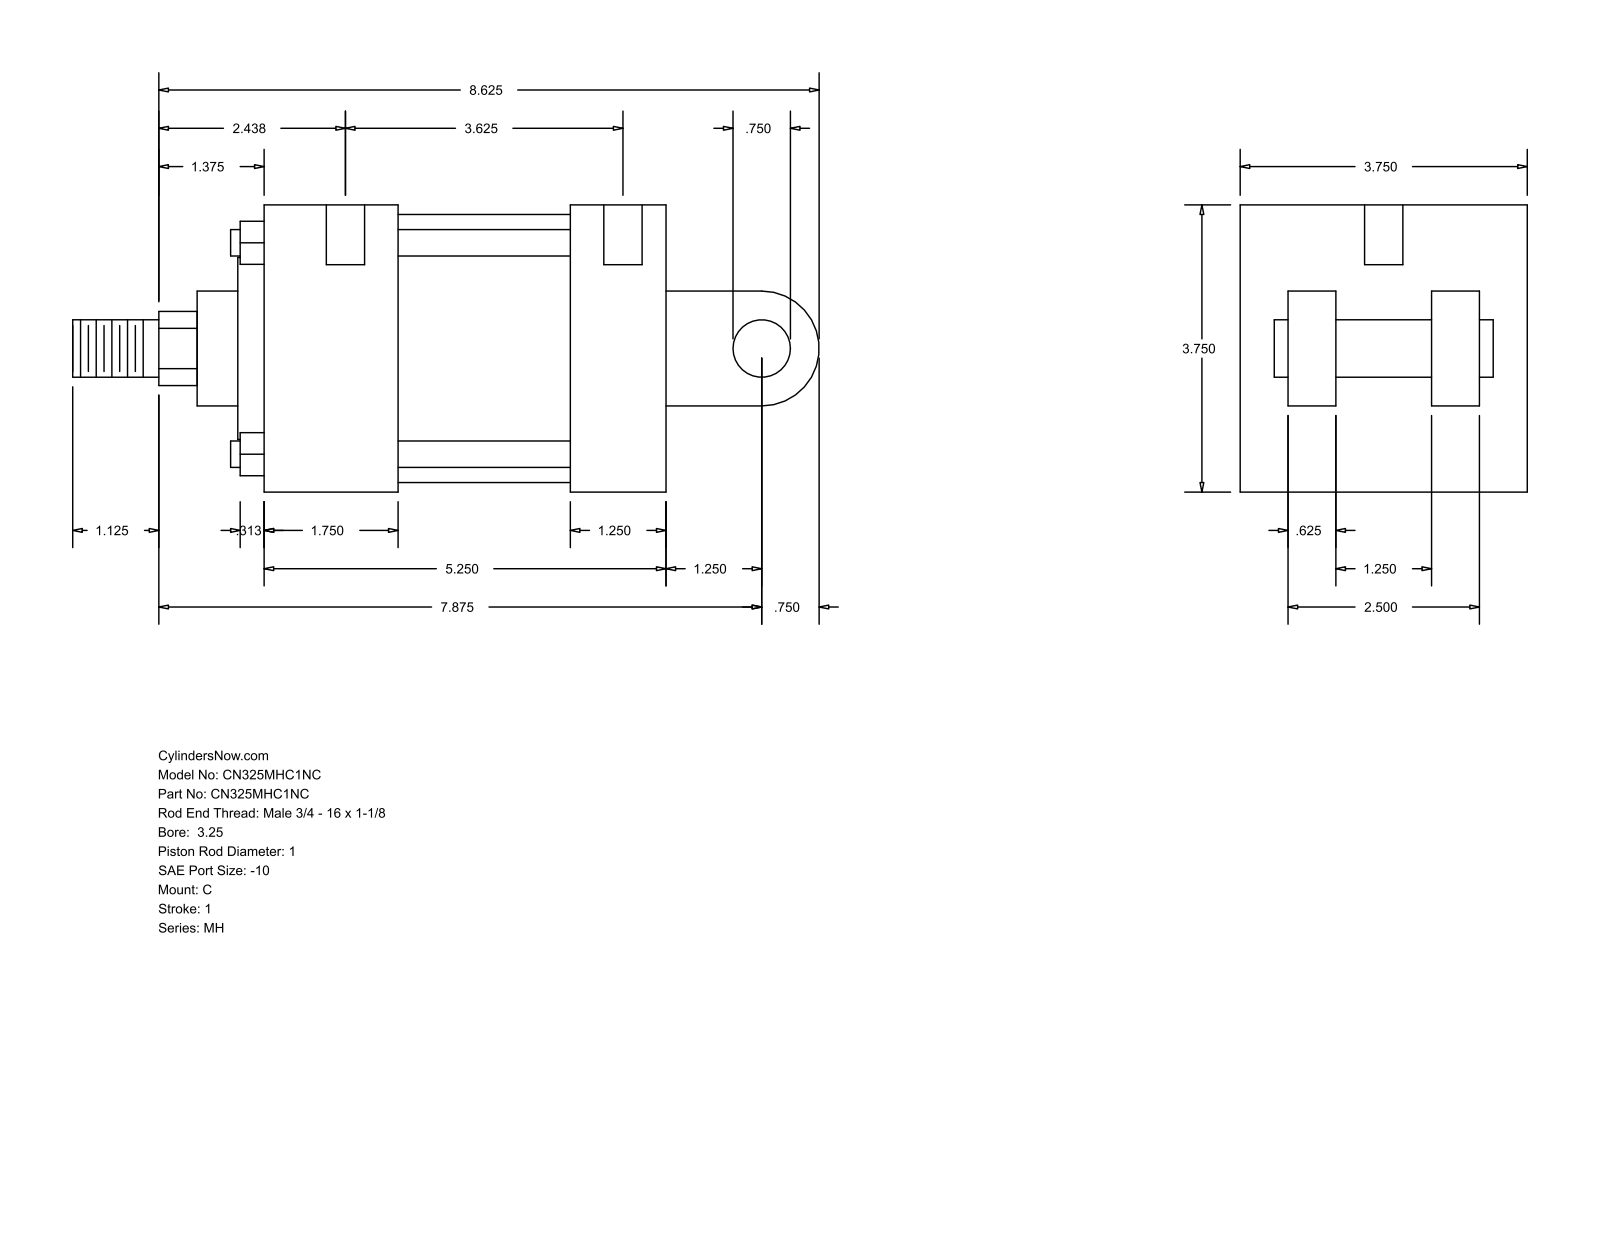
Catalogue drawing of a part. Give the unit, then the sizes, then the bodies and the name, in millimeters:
Units: millimetres
Overall size (bounding box): 247.65 × 95.25 × 95.25
Round holes (diameter × count): ⌀5.56 ×4, ⌀12.7 ×2
Round bosses / shafts (diameter × count): ⌀8.76 ×4, ⌀19.05 ×2, ⌀88.9 ×1, ⌀60.33 ×1, ⌀38.1 ×1, ⌀25.4 ×1
Partial cylindrical surfaces — rounded edges, fillets, slot ends (radius × count): R12.29 ×1, R19.05 ×1
Main face-to-face distances: 95.24, 15.87, 133.36, 63.5, 79.37, 31.74, 47.63, 44.46, 101.61, 57.15
Hole centre spacings: 98.42, 1.58, 4.76, 92.08, 93.66, 96.84
Bodies: 0 solids, 101 faces (71 planar, 30 cylindrical, 0 other)
Part name (STEP PRODUCT): MH_C__0325_1
STEP written by: GSSL Pune (CONFIG_CONTROL_DESIGN)
